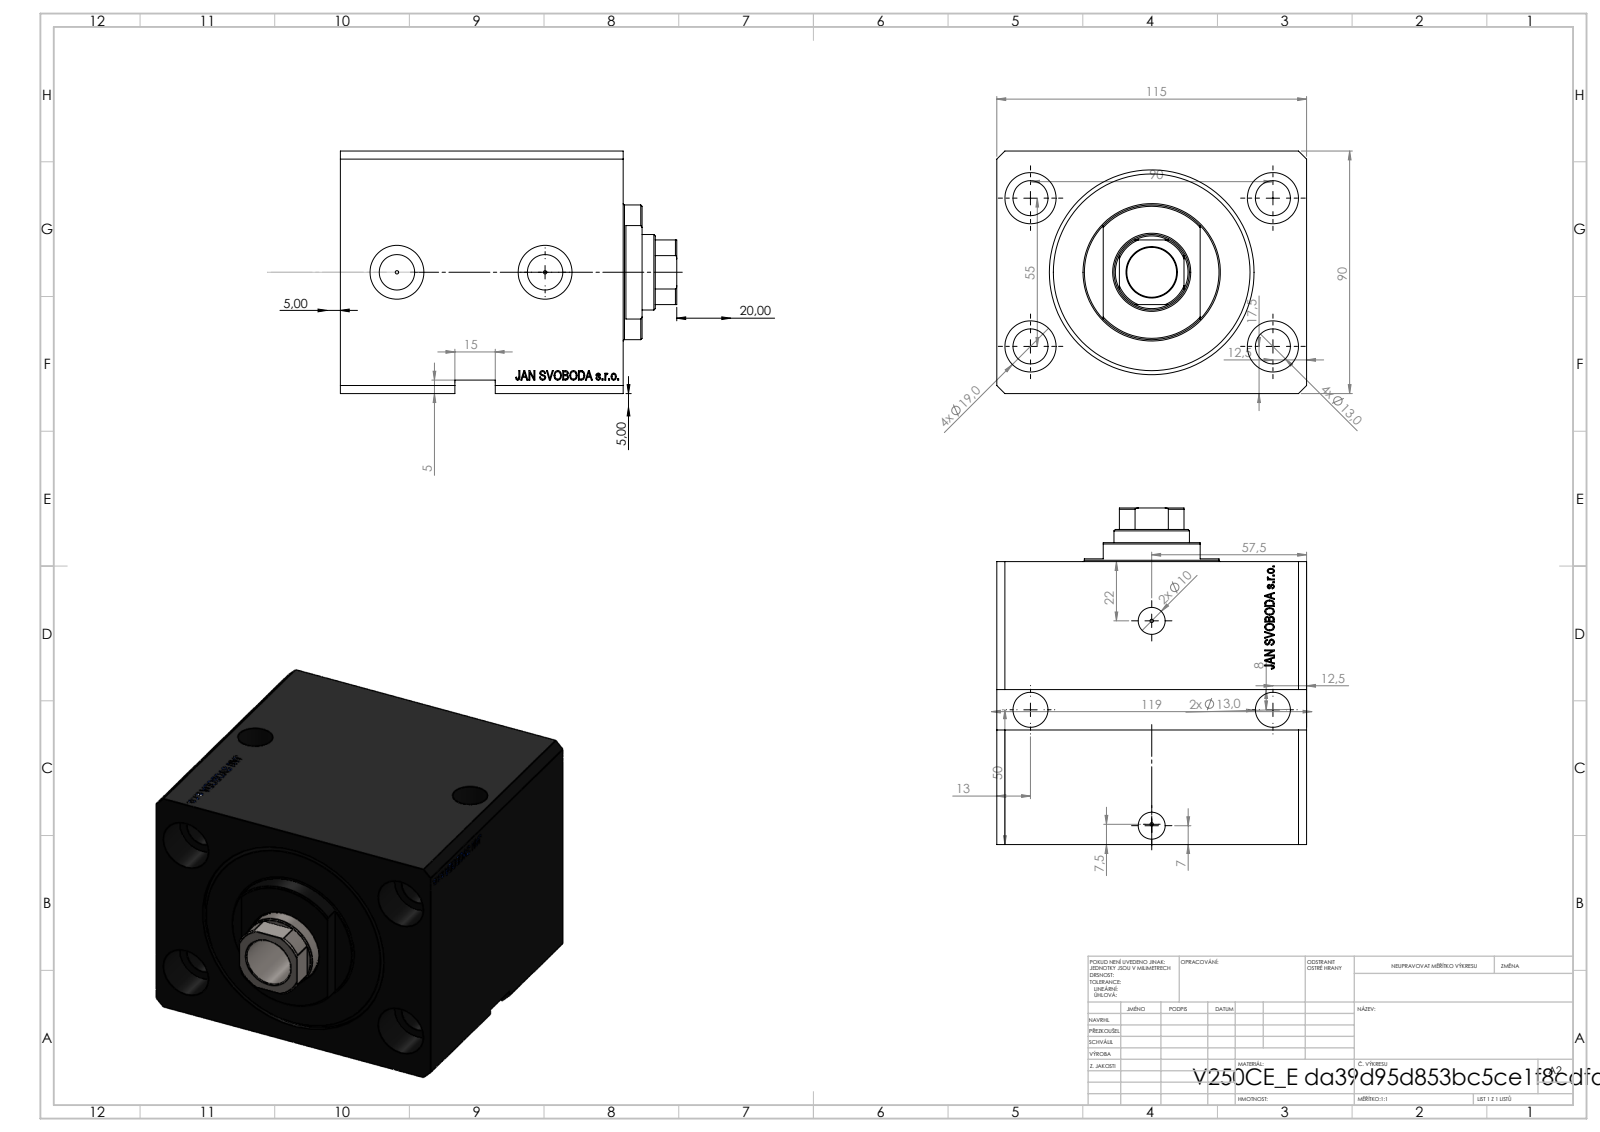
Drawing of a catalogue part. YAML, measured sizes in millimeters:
part_name: "V250CE_VC_E; V250CE_C_VCP; V250CE_E_Body"
step_written_by: "SolidWorks 2019 (CONFIG_CONTROL_DESIGN)"
units: millimeters
bodies: {solids: 3, faces: 937, planar: 467, cylindrical: 84, other: 386}
overall_size: [125, 115, 90]
volume: 942975
surface_area: 144200
round_holes:
  - {diameter: 13, count: 6}
  - {diameter: 1.25, count: 4}
  - {diameter: 19, count: 4}
  - {diameter: 10, count: 2}
  - {diameter: 13.16, count: 2}
  - {diameter: 20, count: 2}
  - {diameter: 18.5, count: 1}
  - {diameter: 28, count: 1}
  - {diameter: 63, count: 1}
  - {diameter: 76, count: 1}
round_bosses_or_shafts:
  - {diameter: 50, count: 1}
partial_cylinders:
  - {radius: 13.5, count: 1}
face_to_face_distances: [90, 20, 115, 85, 105, 87.1, 17.9, 67.1, 40, 65]
hole_center_spacings: [52.74, 55, 90, 55.8, 61.88, 62.24, 105.48, 0.53]
